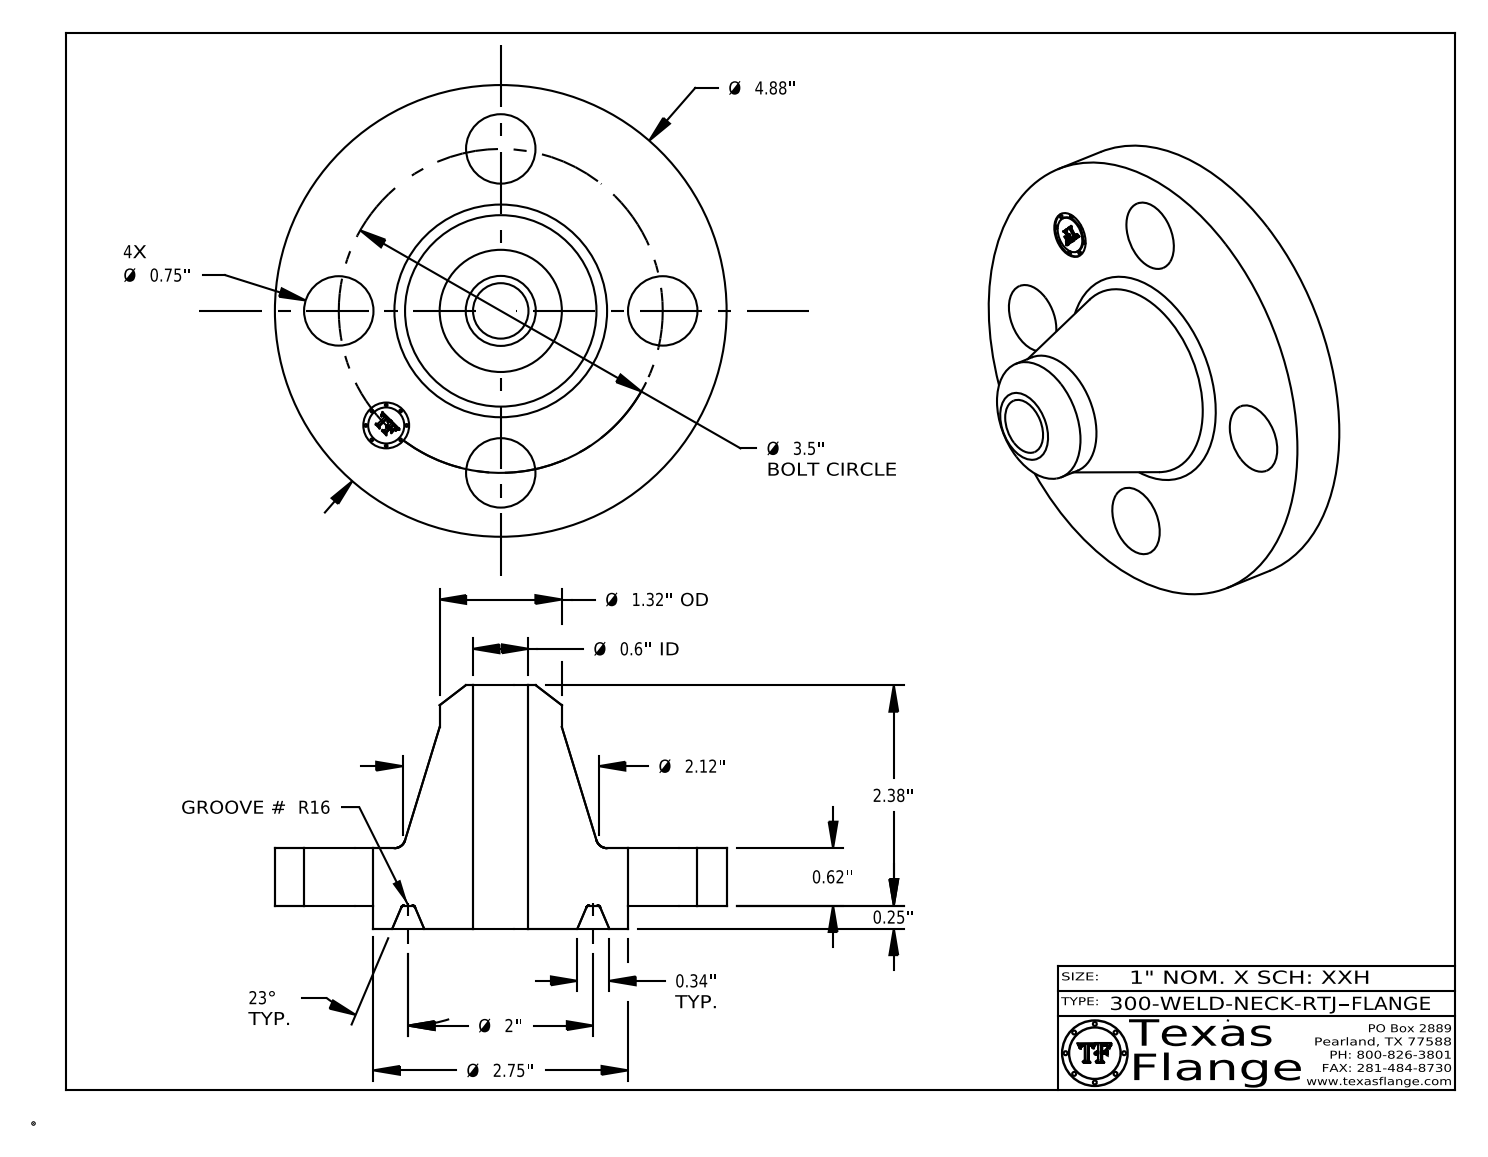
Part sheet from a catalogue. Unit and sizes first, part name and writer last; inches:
Units: inches
Overall size (bounding box): 4.88 × 4.88 × 2.63
Round holes (diameter × count): ⌀0.75 ×4, ⌀0.495 ×1, ⌀0.599 ×1
Round bosses / shafts (diameter × count): ⌀0.03 ×8, ⌀4.88 ×1, ⌀2.75 ×1, ⌀1.32 ×1, ⌀0.39 ×1
Main face-to-face distances: 0.62, 0.25, 0.87, 2.63, 2.38, 1.76, 0.015, 0.855, 0.605, 1.775
Hole centre spacings: 1.75, 2.475, 1.339, 3.233, 3.5
Volume: 14.48 in³ · Surface area: 64.17 in²
Bodies: 1 solid, 421 faces (371 planar, 36 cylindrical, 14 other)
Part name (STEP PRODUCT): 300-WELD-NECK-RTJ
STEP written by: CATIA V5 STEP AP214 (AUTOMOTIVE_DESIGN)
